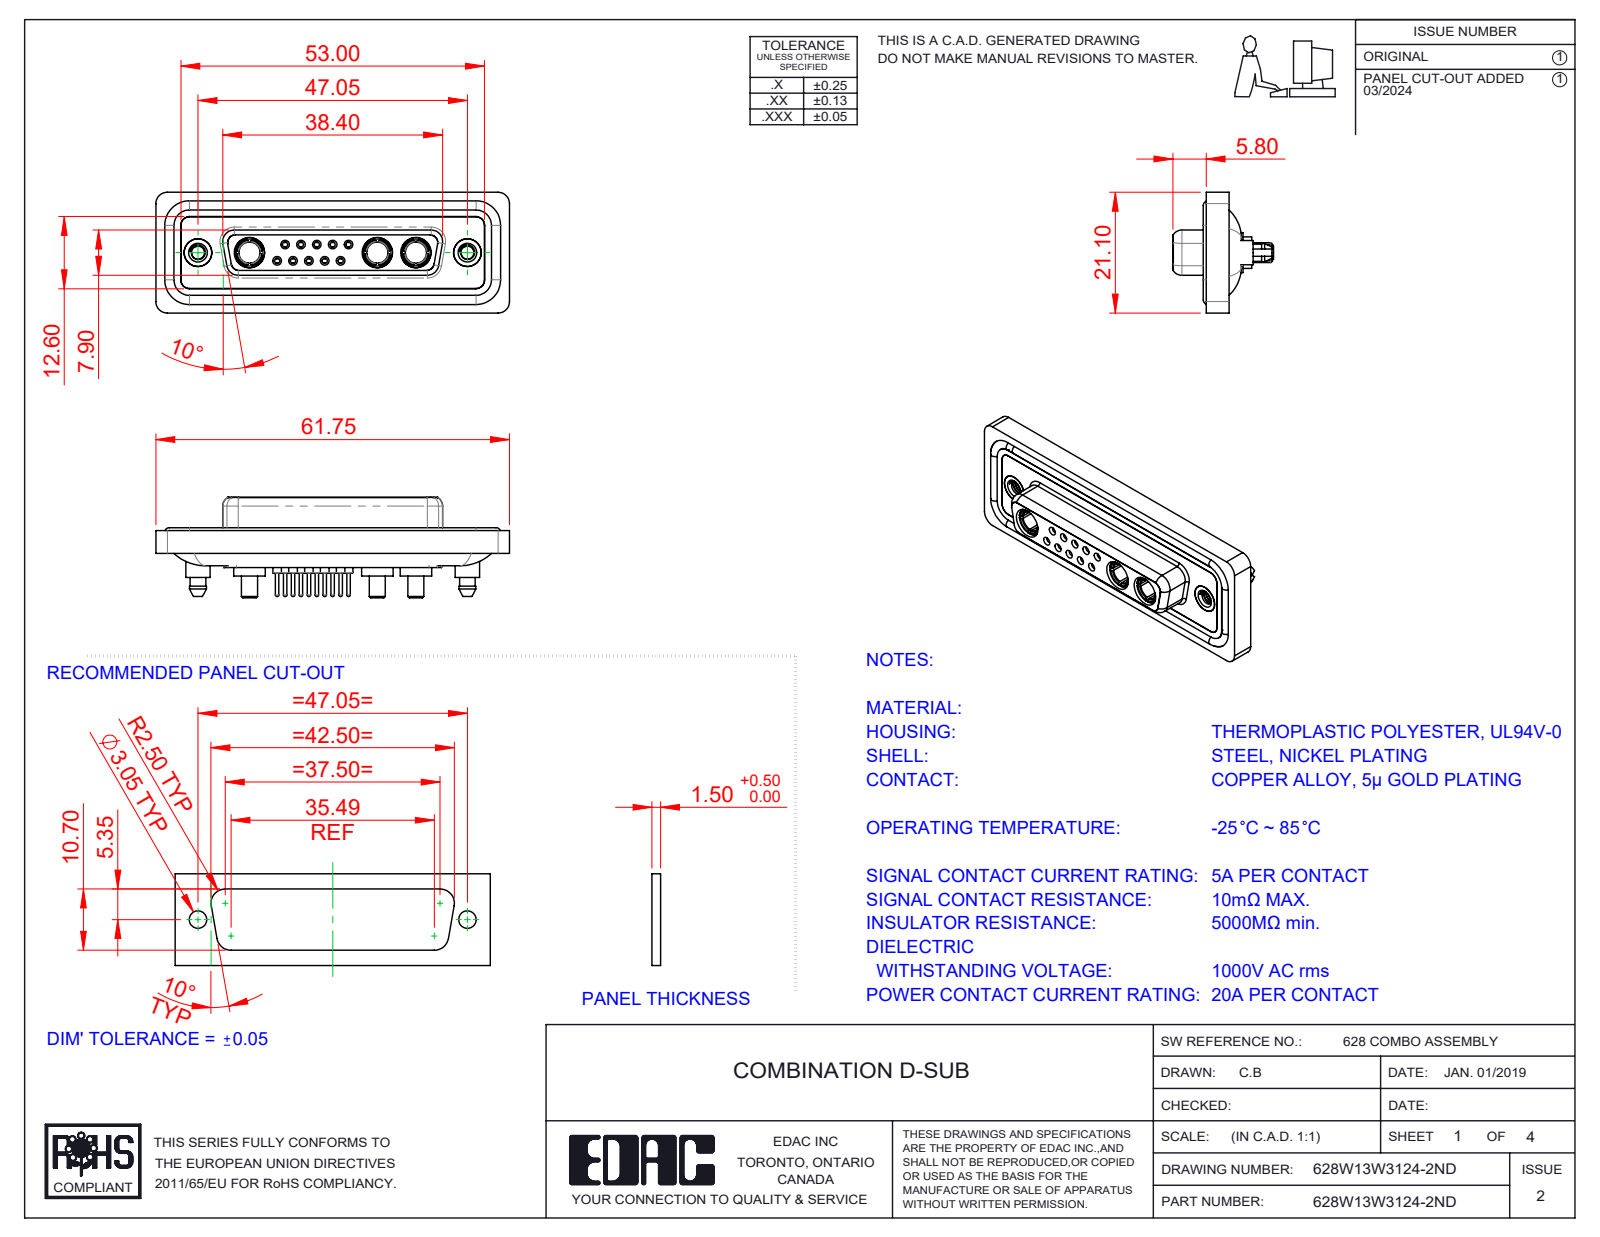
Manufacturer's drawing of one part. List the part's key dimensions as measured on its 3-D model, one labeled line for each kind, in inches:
Part name (STEP PRODUCT): 628W13W3124-2ND; 628Combo Threaded Boardlock_D; 628Combo Contact Row 2_24; 628Combo Shell Front_25 Contacts (+5 more)
STEP written by: SolidWorks 2023 (CONFIG_CONTROL_DESIGN)
Units: inches
Bodies: 23 solids, 1224 faces (358 planar, 495 cylindrical, 371 other)
Overall size (bounding box): 2.431 × 0.831 × 0.691
Volume: 0.513 in³ · Surface area: 21.77 in²
Round holes (diameter × count): ⌀0.035 ×10, ⌀0.043 ×10, ⌀0.059 ×10, ⌀0.079 ×10, ⌀0.063 ×5, ⌀0.067 ×5, ⌀0.191 ×5, ⌀0.146 ×3, ⌀0.209 ×3, ⌀0.089 ×2, ⌀0.157 ×2, ⌀0.159 ×2
Round bosses / shafts (diameter × count): ⌀0.087 ×10, ⌀0.024 ×10, ⌀0.063 ×9, ⌀0.217 ×3, ⌀0.205 ×3, ⌀0.195 ×3, ⌀0.187 ×3, ⌀0.148 ×3
Partial cylindrical surfaces — rounded edges, fillets, slot ends (radius × count): R0.059 ×24, R0.079 ×18, R0.063 ×10, R0.053 ×8, R0.01 ×4, R0.02 ×4, R0.024 ×4, R0.026 ×4
Main face-to-face distances: 0.016, 0.071, 0.293, 0.222, 0.02, 0.26, 0.278, 0.063, 0.114, 0.043
Hole centre spacings: 0.124, 0.109, 0.198, 0.198, 0.218, 0.327, 0.295, 0.109
